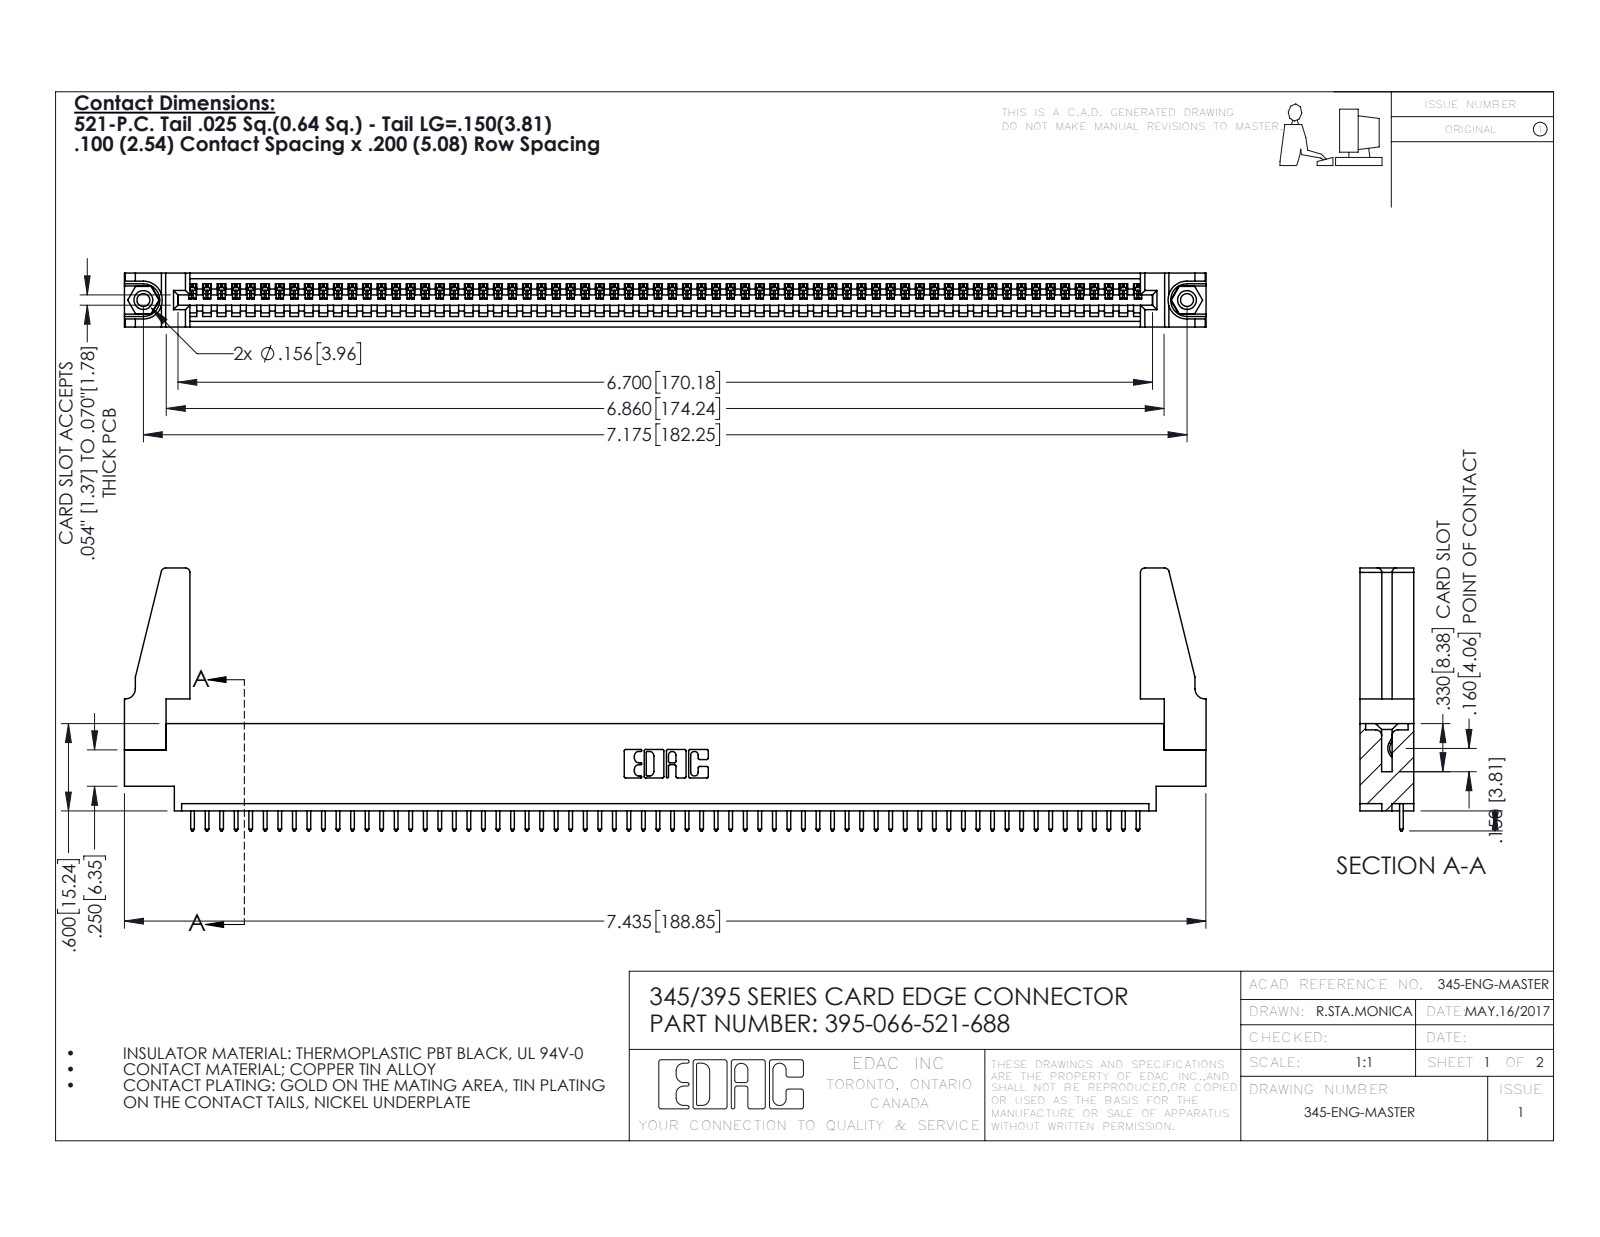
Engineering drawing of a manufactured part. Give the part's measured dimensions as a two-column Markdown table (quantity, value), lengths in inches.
| quantity | value |
| --- | --- |
| part name | 395-066-521-688; 345-292-001_345-293-121; 345 Part_0.170 Offset - 0.156 Dia-TH; 345-220-078_345-220-088 (+1 more) |
| STEP written by | SolidWorks 2016 (CONFIG_CONTROL_DESIGN) |
| units | inches |
| bodies | 71 solids, 4082 faces (2796 planar, 1270 cylindrical, 16 other) |
| overall size | 7.436 × 1.807 × 0.37 |
| volume | 1.287 in³ |
| surface area | 41.15 in² |
| round holes (diameter × count) | 0.089 × 2, 0.125 × 2, 0.156 × 2, 0.064 × 1 |
| round bosses / shafts (diameter × count) | 0.155 × 2 |
| partial cylindrical surfaces (radius × count) | 0.006 × 132, 0.01 × 132, 0.01 × 22, 0.03 × 8, 0.007 × 6, 0.031 × 6, 0.026 × 3, 0.031 × 2 |
| main face-to-face distances | 0.072, 0.298, 0.37, 0.098, 0.272, 0.025, 0.2, 0.225, 0.175, 0.149 |
| hole center spacings | 0.27, 6.939, 7.175 |
